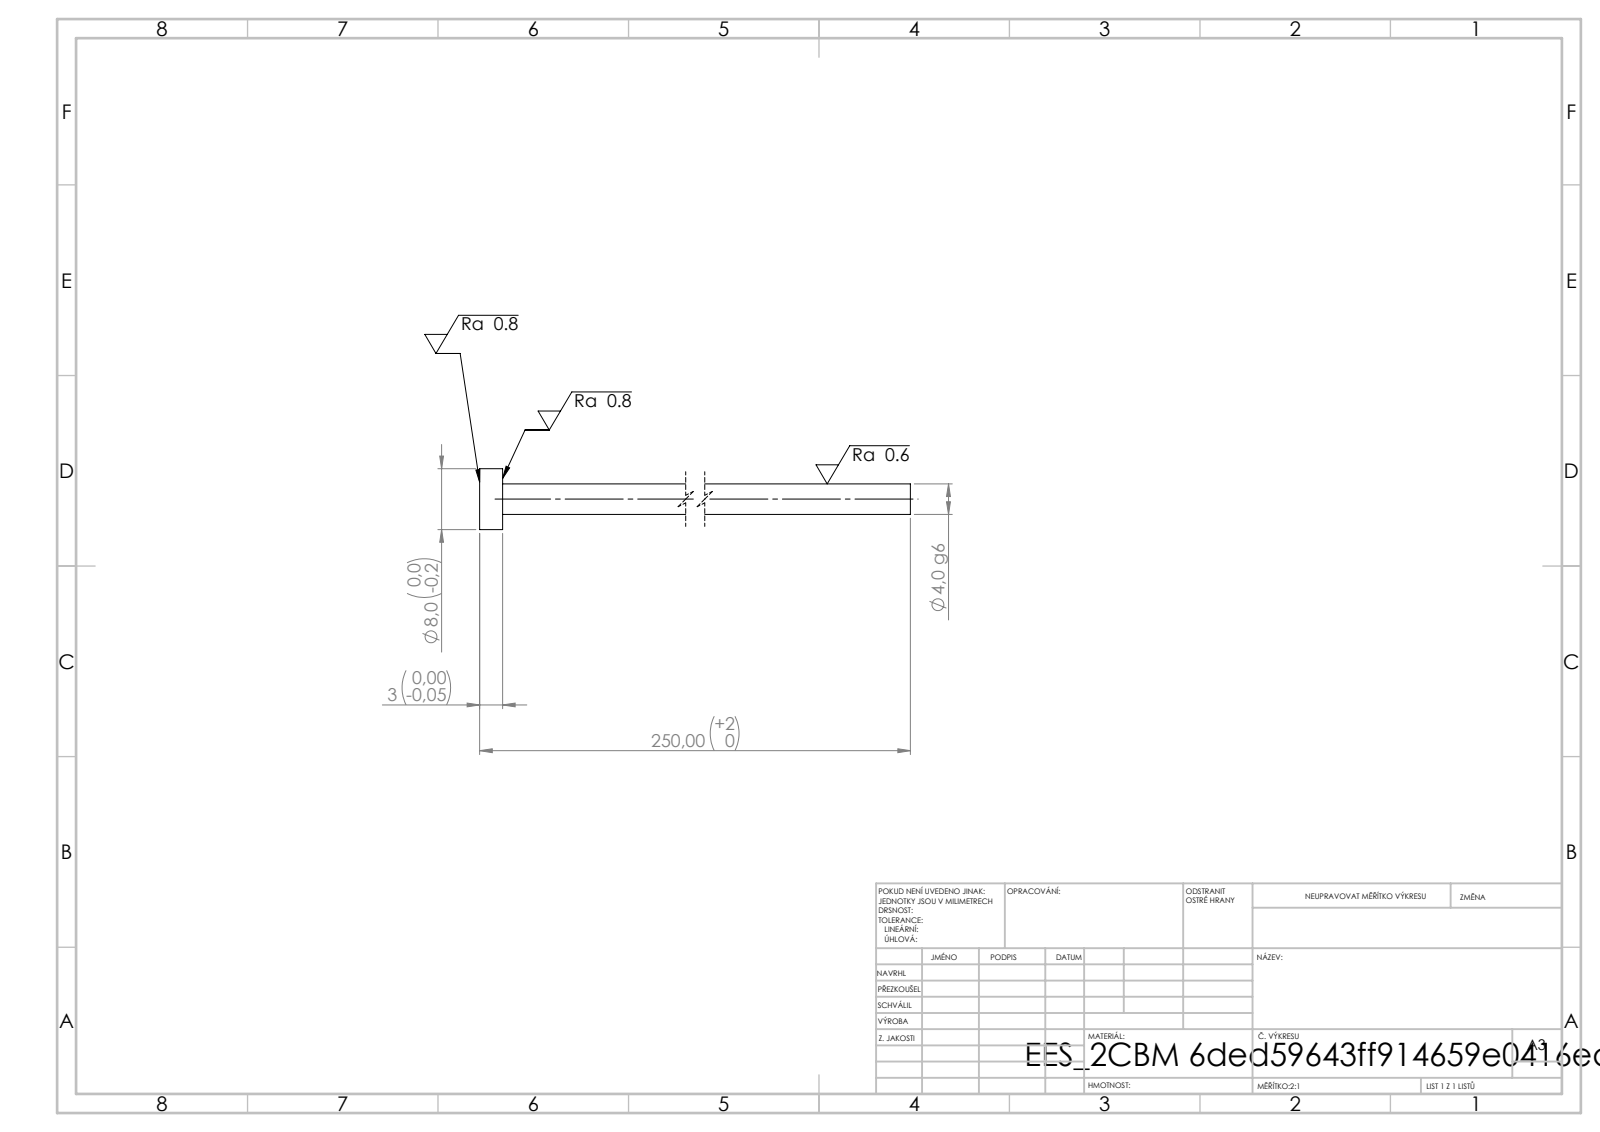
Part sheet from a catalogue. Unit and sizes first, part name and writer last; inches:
Units: inches
Overall size (bounding box): 9.843 × 0.315 × 0.315
Round bosses / shafts (diameter × count): ⌀0.315 ×1, ⌀0.157 ×1
Main face-to-face distances: 0.118, 9.843, 9.724
Volume: 0.199 in³ · Surface area: 5.084 in²
Bodies: 1 solid, 7 faces (3 planar, 4 cylindrical, 0 other)
STEP written by: SolidWorks 2019 (CONFIG_CONTROL_DESIGN)
